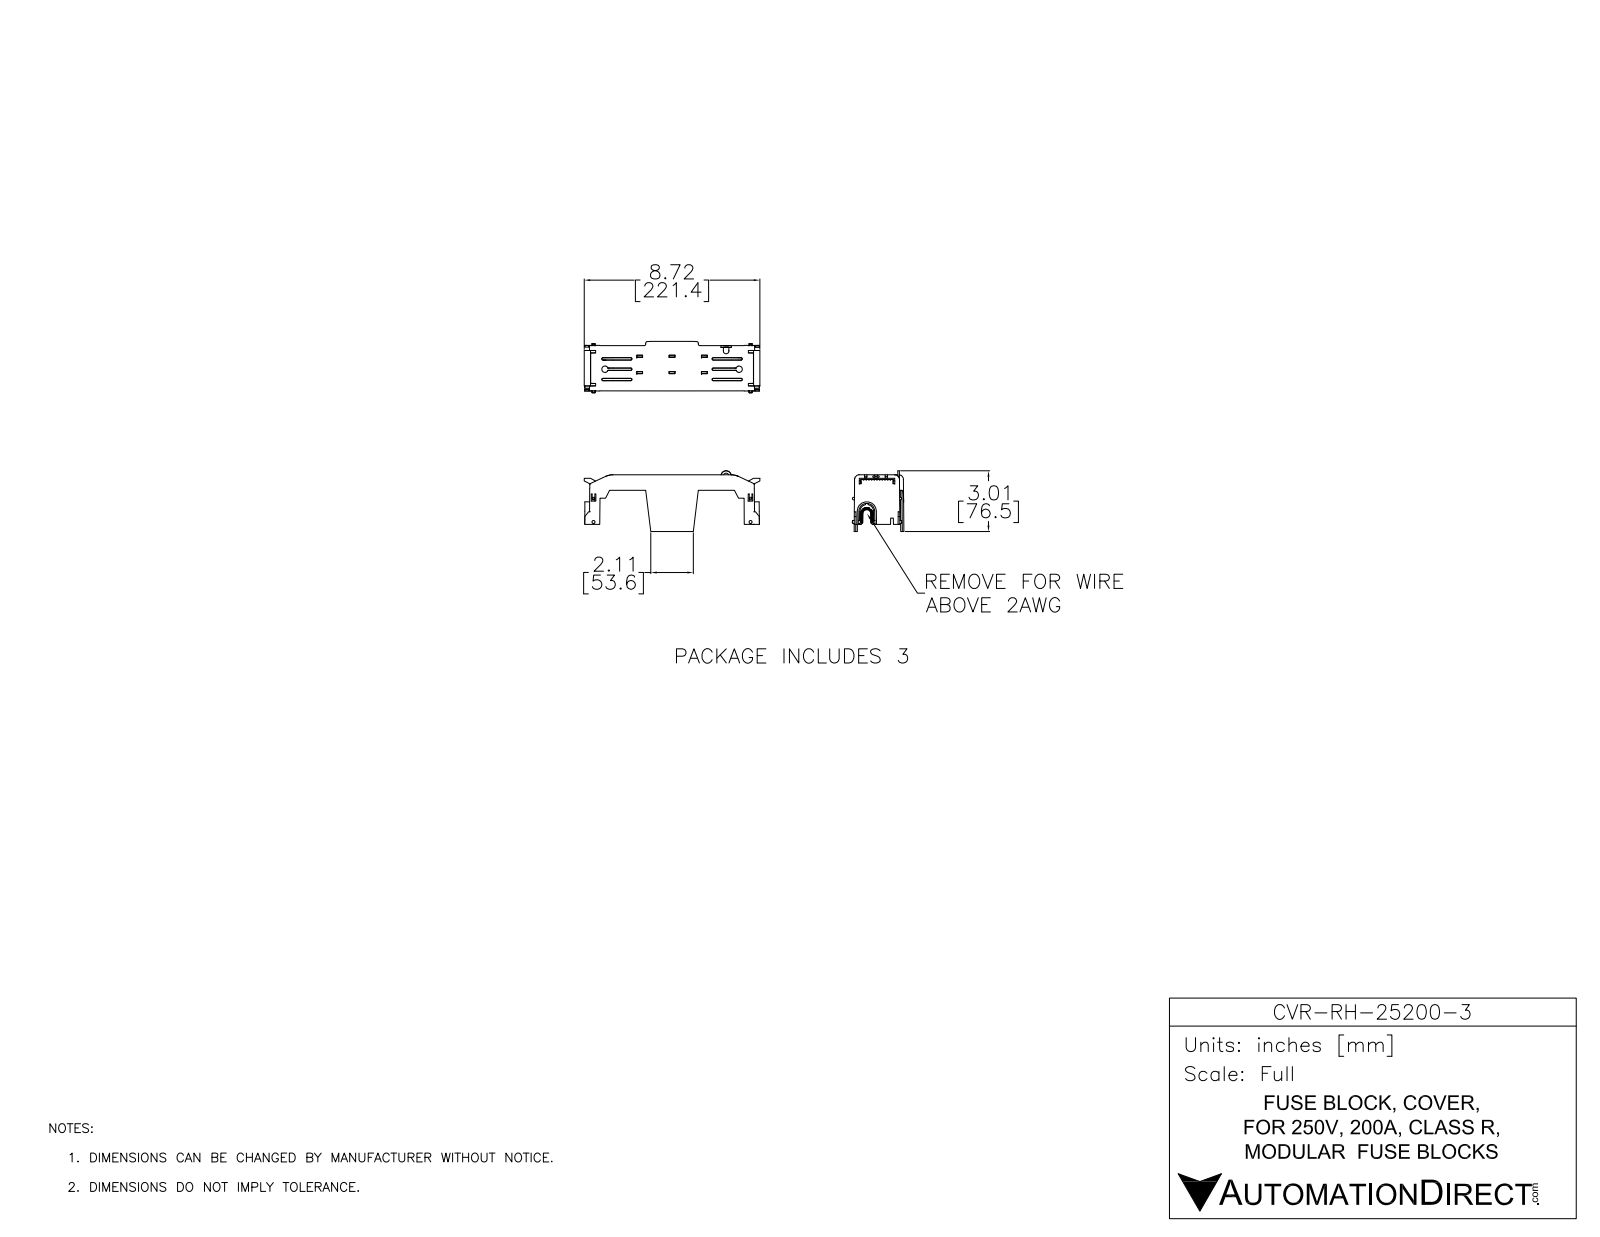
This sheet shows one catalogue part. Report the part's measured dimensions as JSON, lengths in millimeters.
{"part_name": "CVR-RH-25200-3", "step_written_by": "SolidWorks 2017 (AUTOMOTIVE_DESIGN)", "units": "millimeters", "bodies": {"solids": 1, "faces": 1406, "planar": 950, "cylindrical": 105, "other": 351}, "overall_size": [221.4, 76.5, 64.9], "volume_mm3": 75660, "surface_area_mm2": 80650, "round_holes": [[7, 1]], "partial_cylinders_radius": [[1, 16], [6, 9], [3, 8], [4, 7], [2, 6], [0.3, 2], [0.5, 2], [16, 2]], "face_to_face_distances": [2, 5, 3, 7, 20.4, 15.3, 42.2, 44.2, 32.7, 34.7]}
